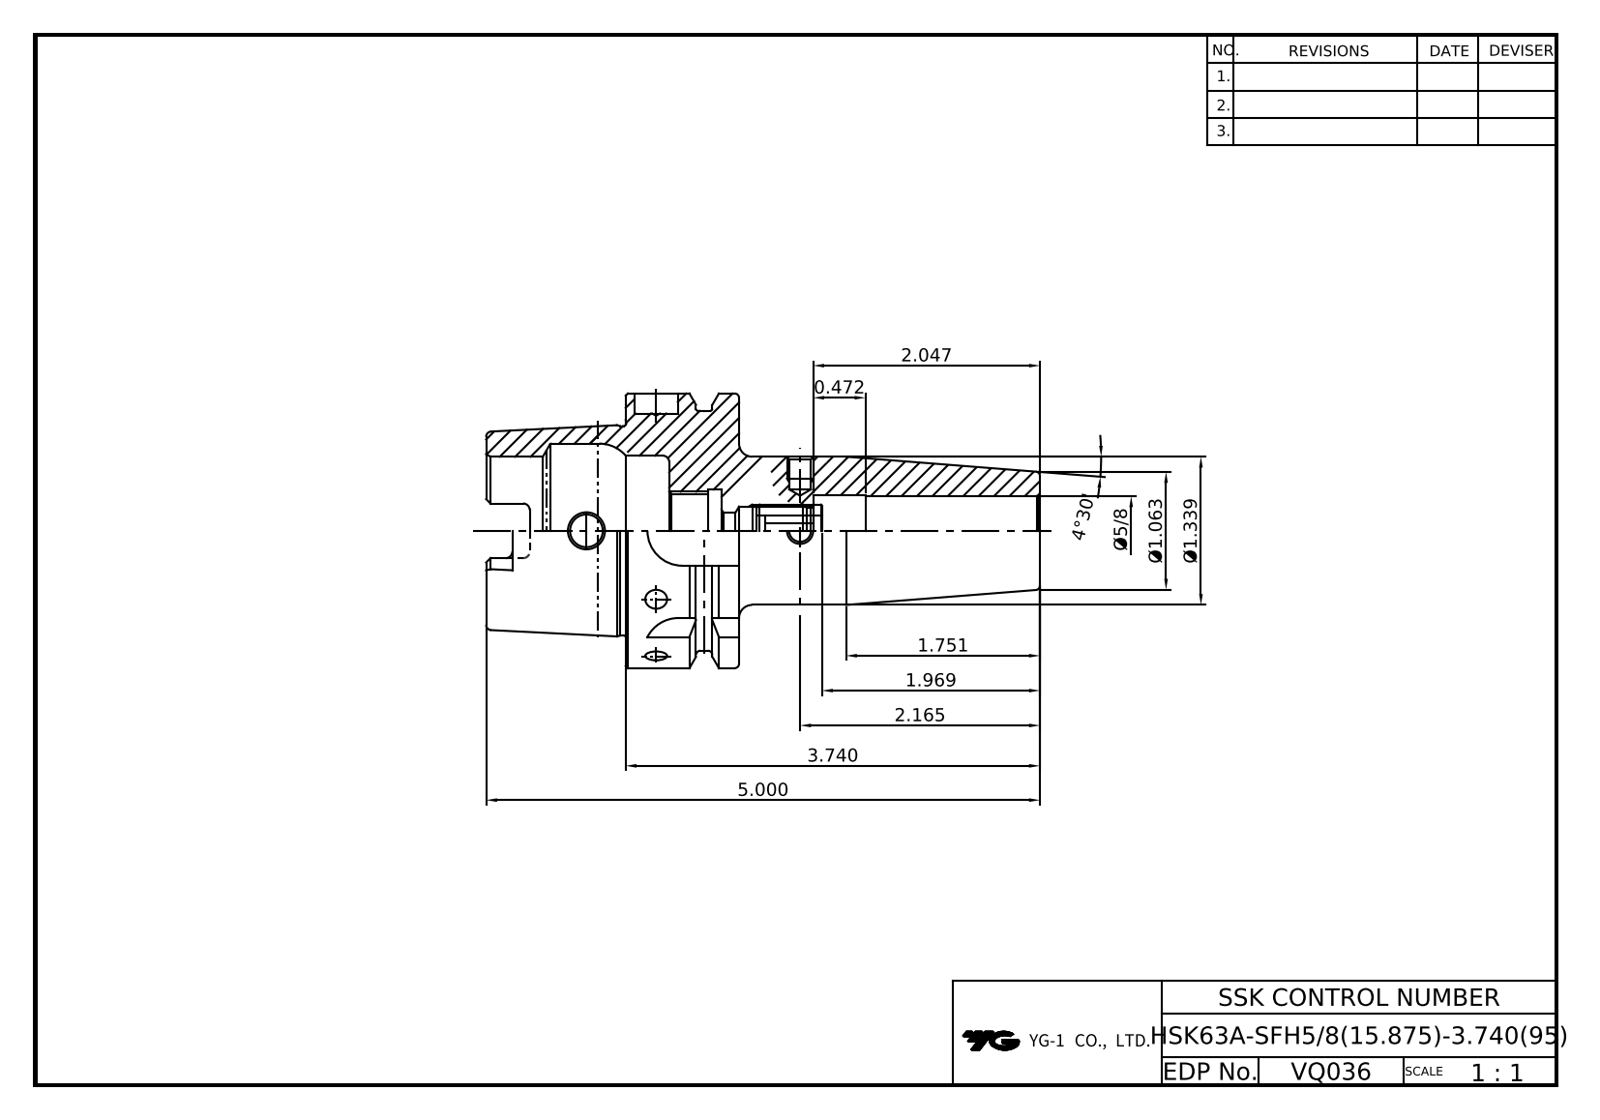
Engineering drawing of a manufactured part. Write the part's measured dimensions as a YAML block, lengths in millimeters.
part_name: "LO-HSK63A-SFH15.875-95"
step_written_by: "Autodesk Inventor 2022 (AUTOMOTIVE_DESIGN)"
units: millimeters
bodies: {solids: 1, faces: 116, planar: 42, cylindrical: 34, other: 40}
overall_size: [127, 63, 63]
volume: 124279
surface_area: 31942
round_holes:
  - {diameter: 7.5, count: 1}
  - {diameter: 8.4, count: 1}
  - {diameter: 10, count: 1}
  - {diameter: 10.92, count: 1}
  - {diameter: 15.87, count: 1}
  - {diameter: 16.92, count: 1}
  - {diameter: 17.07, count: 1}
  - {diameter: 19, count: 1}
  - {diameter: 34, count: 1}
  - {diameter: 40, count: 1}
round_bosses_or_shafts:
  - {diameter: 63, count: 1}
  - {diameter: 55, count: 1}
  - {diameter: 48.04, count: 1}
partial_cylinders:
  - {radius: 1.5, count: 6}
  - {radius: 2.88, count: 4}
  - {radius: 8, count: 4}
face_to_face_distances: [26, 10, 16, 32, 42, 58, 69, 53, 12, 127]
